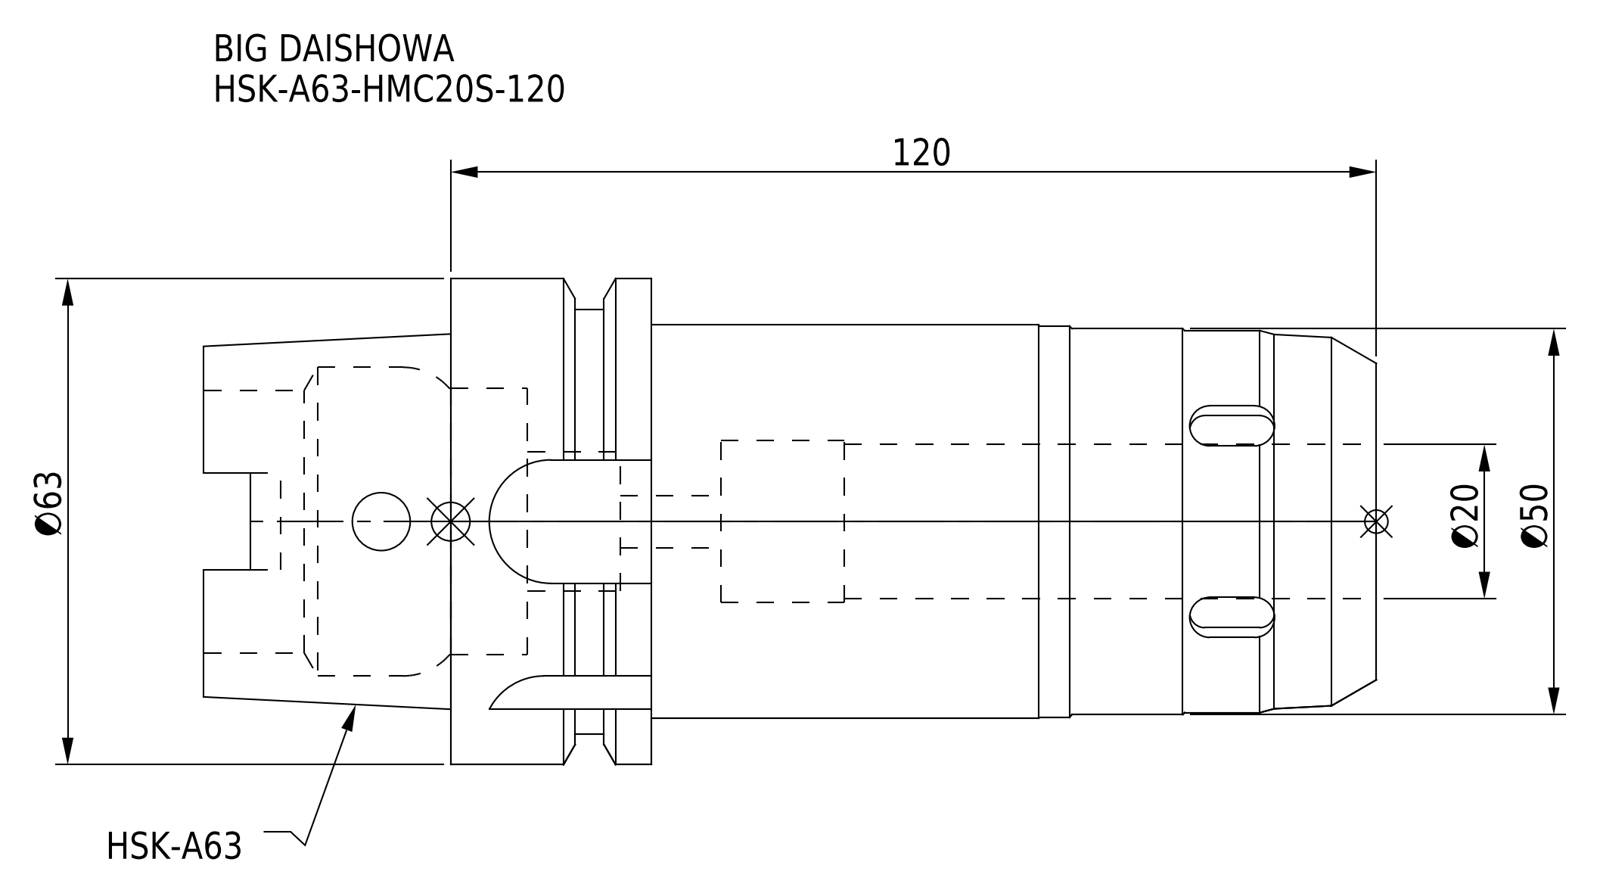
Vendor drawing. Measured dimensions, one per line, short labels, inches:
name: HSK-A63-HMC20S-120
written by: CREO PARAMETRIC BY PTC INC, 2016380 (AUTOMOTIVE_DESIGN)
unit: in
bodies: 1 solid, 138 faces (57 planar, 55 cylindrical, 26 other)
size: 5.984 × 2.48 × 2.48
volume: 14.53 in³; area: 66.06 in²
holes: 1× ⌀0.266, 1× ⌀0.295, 1× ⌀0.709, 1× ⌀0.787, 1× ⌀0.827, 1× ⌀1.339, 1× ⌀1.358, 1× ⌀1.575
bosses: 1× ⌀2.48, 1× ⌀2.165, 1× ⌀2.008, 1× ⌀1.996, 1× ⌀1.969, 1× ⌀1.949
rounds: 6× R0.118, 4× R0.113, 4× R0.315
face distances: 4.724, 1.024, 3.701, 4.333, 0.632, 0.392, 5.984, 2.283, 1.652, 1.26
